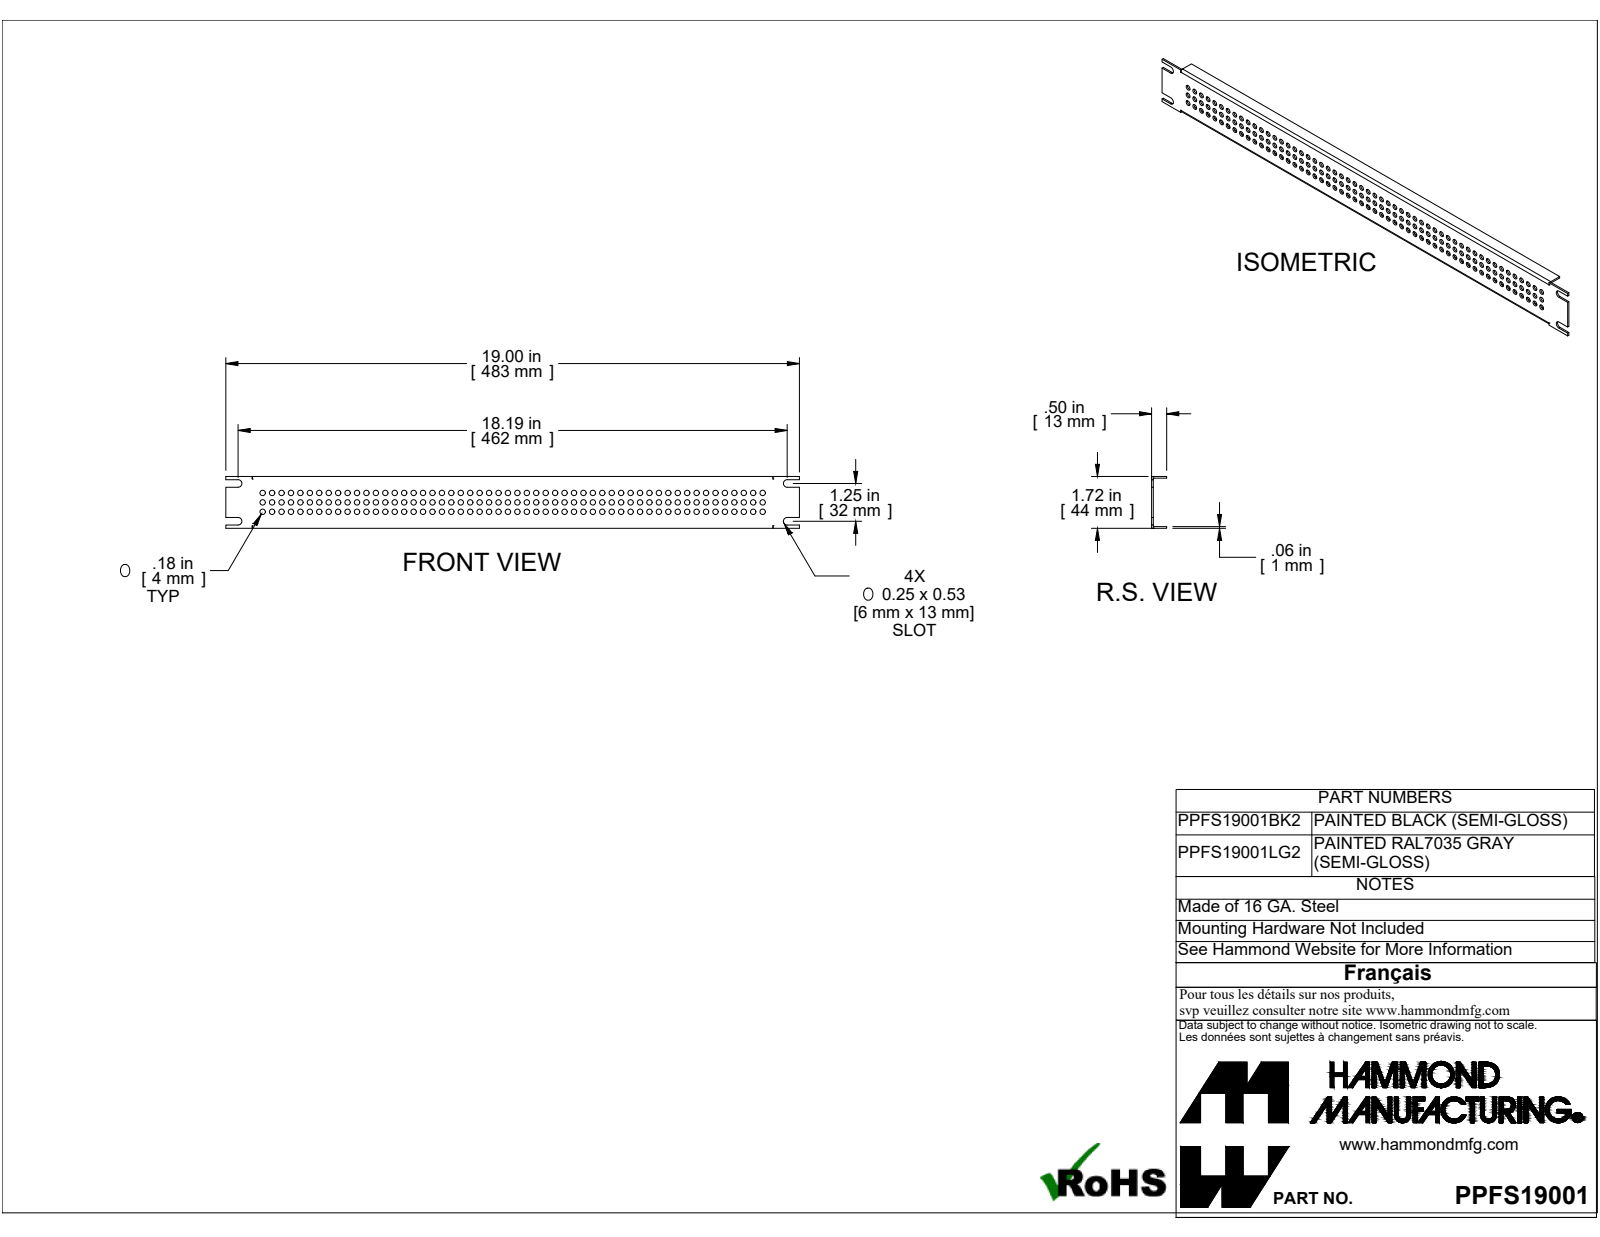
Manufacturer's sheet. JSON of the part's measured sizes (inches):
{"part_name": "PPFS19001LG2", "step_written_by": "SolidWorks 2019 (CONFIG_CONTROL_DESIGN)", "units": "inches", "bodies": {"solids": 1, "faces": 208, "planar": 38, "cylindrical": 170, "other": 0}, "overall_size": [19, 1.718, 0.5], "volume_in3": 2.427, "surface_area_in2": 93.02, "round_holes": [[0.177, 162]], "partial_cylinders_radius": [[0.125, 4], [0.029, 2], [0.086, 2]], "face_to_face_distances": [0.057, 1.661, 1.718, 1.604, 0.5, 0.443, 0.875, 18.125, 0.109, 0.359], "hole_center_spacings": [0.699, 0.313, 0.442, 1.289, 0.625, 0.988, 1.25, 1.594]}
